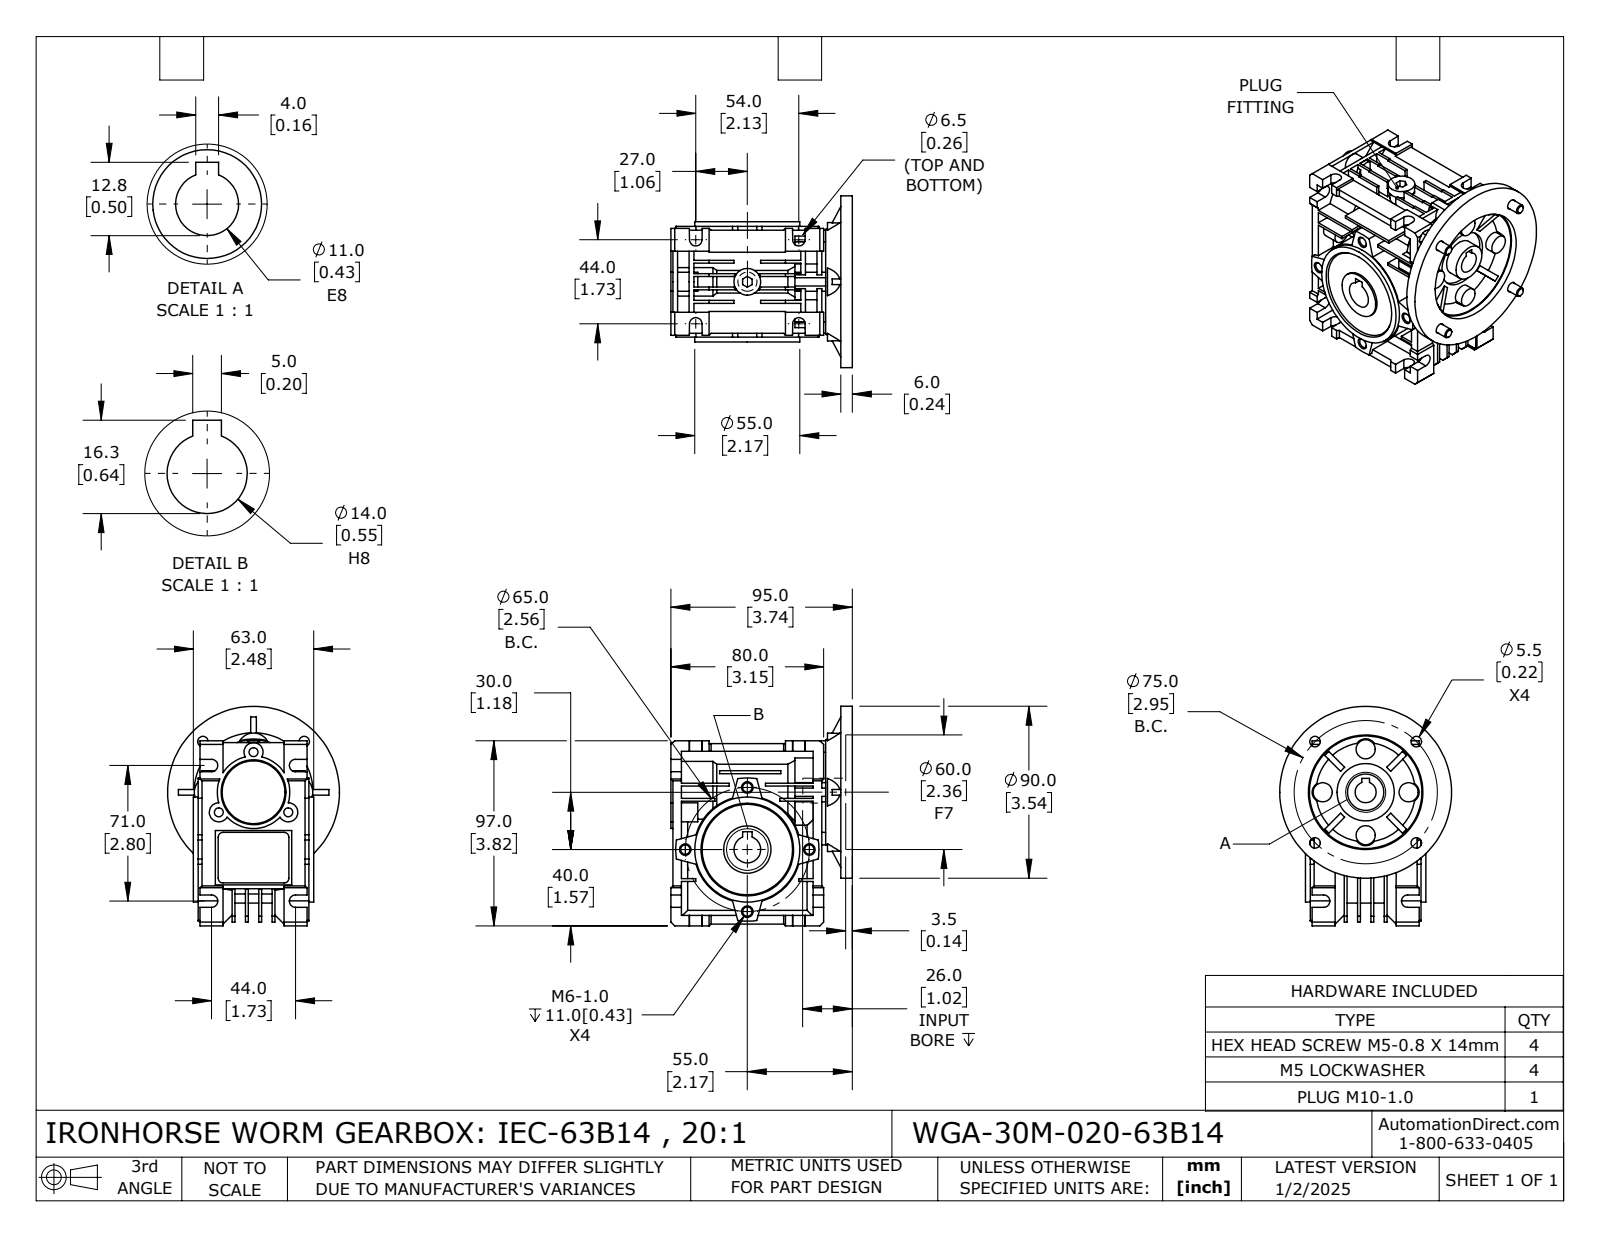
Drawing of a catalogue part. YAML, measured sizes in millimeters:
part_name: "WGA-30M-020-63B14"
step_written_by: "SolidWorks 2024 (CONFIG_CONTROL_DESIGN)"
units: millimeters
bodies: {solids: 14, faces: 905, planar: 566, cylindrical: 239, other: 100}
overall_size: [115, 101.7, 90]
volume: 339639
surface_area: 112960
round_holes:
  - {diameter: 4.92, count: 4}
  - {diameter: 5.1, count: 4}
  - {diameter: 5.5, count: 4}
  - {diameter: 4.65, count: 3}
  - {diameter: 4.92, count: 2}
  - {diameter: 9, count: 1}
  - {diameter: 11, count: 1}
  - {diameter: 11.5, count: 1}
  - {diameter: 14, count: 1}
  - {diameter: 14.5, count: 1}
  - {diameter: 19, count: 1}
  - {diameter: 24.8, count: 1}
round_bosses_or_shafts:
  - {diameter: 10, count: 4}
  - {diameter: 9.2, count: 4}
  - {diameter: 5, count: 4}
  - {diameter: 90, count: 1}
  - {diameter: 56, count: 1}
  - {diameter: 55, count: 1}
  - {diameter: 38, count: 1}
  - {diameter: 37, count: 1}
partial_cylinders:
  - {radius: 3.25, count: 8}
  - {radius: 2.5, count: 4}
  - {radius: 5.5, count: 4}
  - {radius: 8.5, count: 4}
  - {radius: 5, count: 3}
  - {radius: 7.5, count: 1}
  - {radius: 17, count: 1}
  - {radius: 21.5, count: 1}
face_to_face_distances: [1.5, 7, 5.5, 1, 14, 4.5, 8.5, 6, 10, 2]
hole_center_spacings: [32.5, 37.5, 45.96, 53.04, 21, 18.06, 27.09, 36.37]
